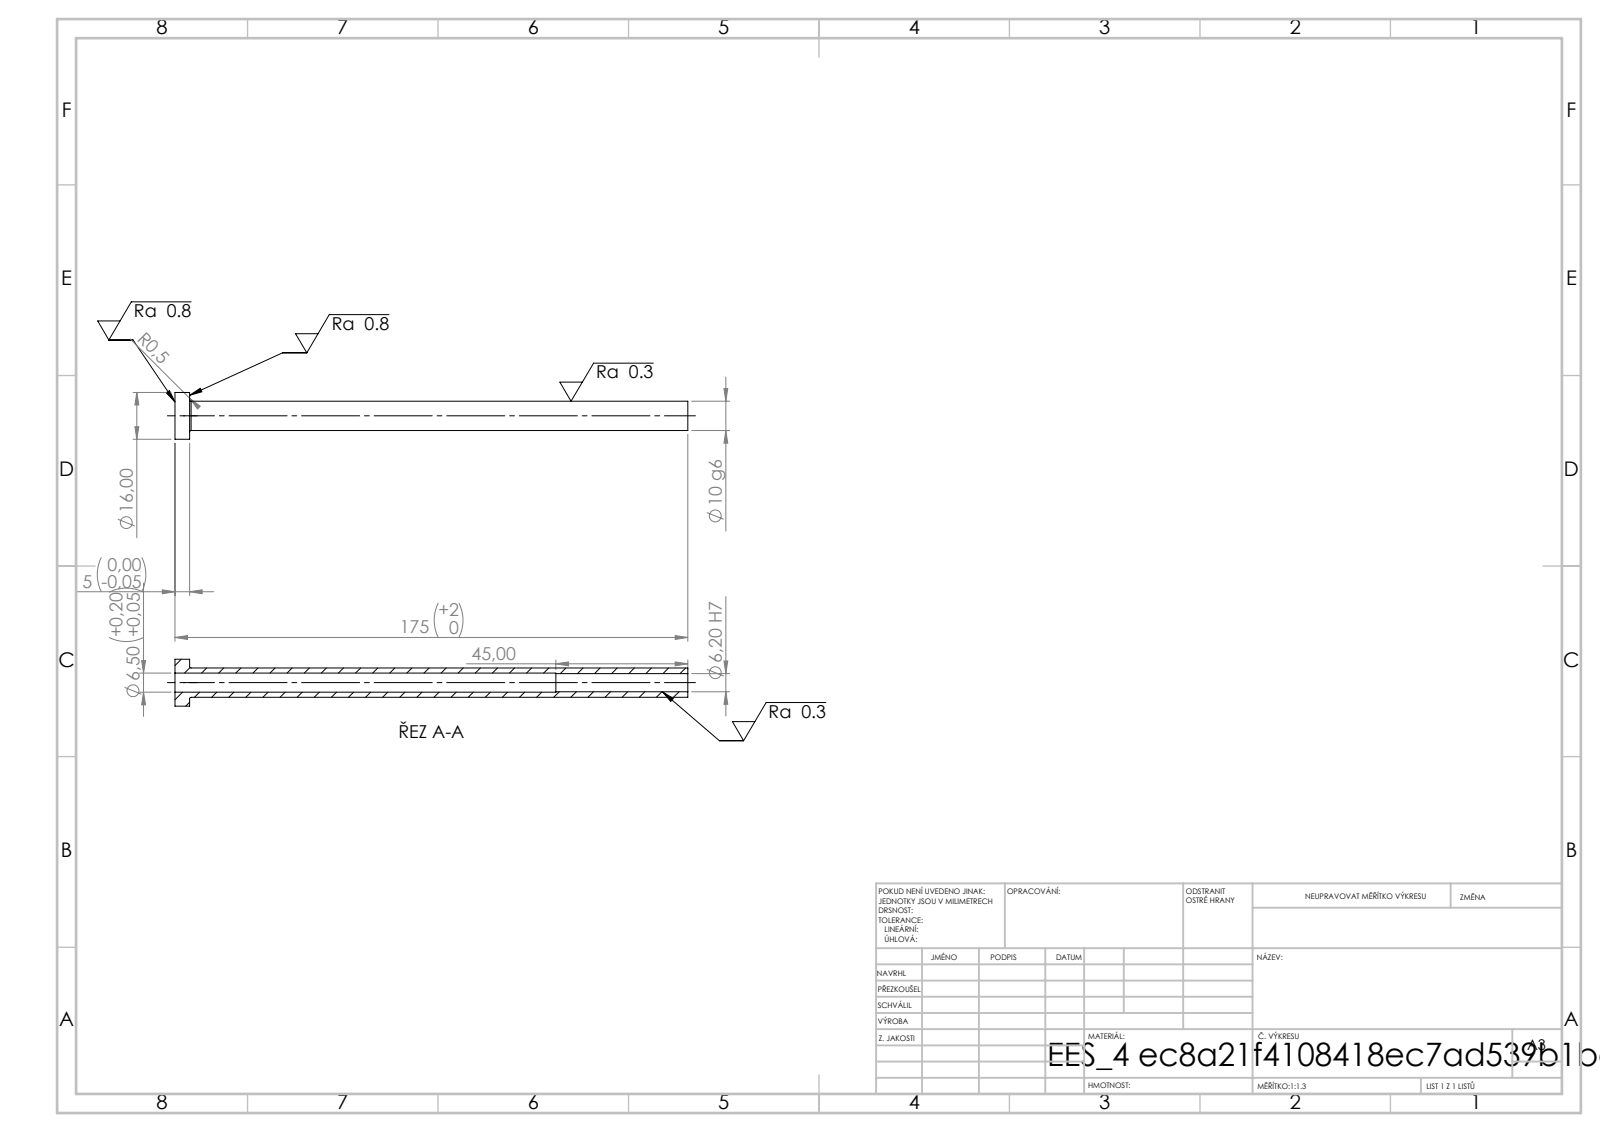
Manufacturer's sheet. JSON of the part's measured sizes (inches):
{"step_written_by": "SolidWorks 2019 (CONFIG_CONTROL_DESIGN)", "units": "inches", "bodies": {"solids": 1, "faces": 14, "planar": 4, "cylindrical": 8, "other": 2}, "overall_size": [6.89, 0.63, 0.63], "volume_in3": 0.53, "surface_area_in2": 14.66, "round_holes": [[0.244, 1], [0.256, 1]], "round_bosses_or_shafts": [[0.63, 1], [0.394, 1]], "face_to_face_distances": [0.197, 6.89, 6.693, 5.118, 4.921, 1.772]}
